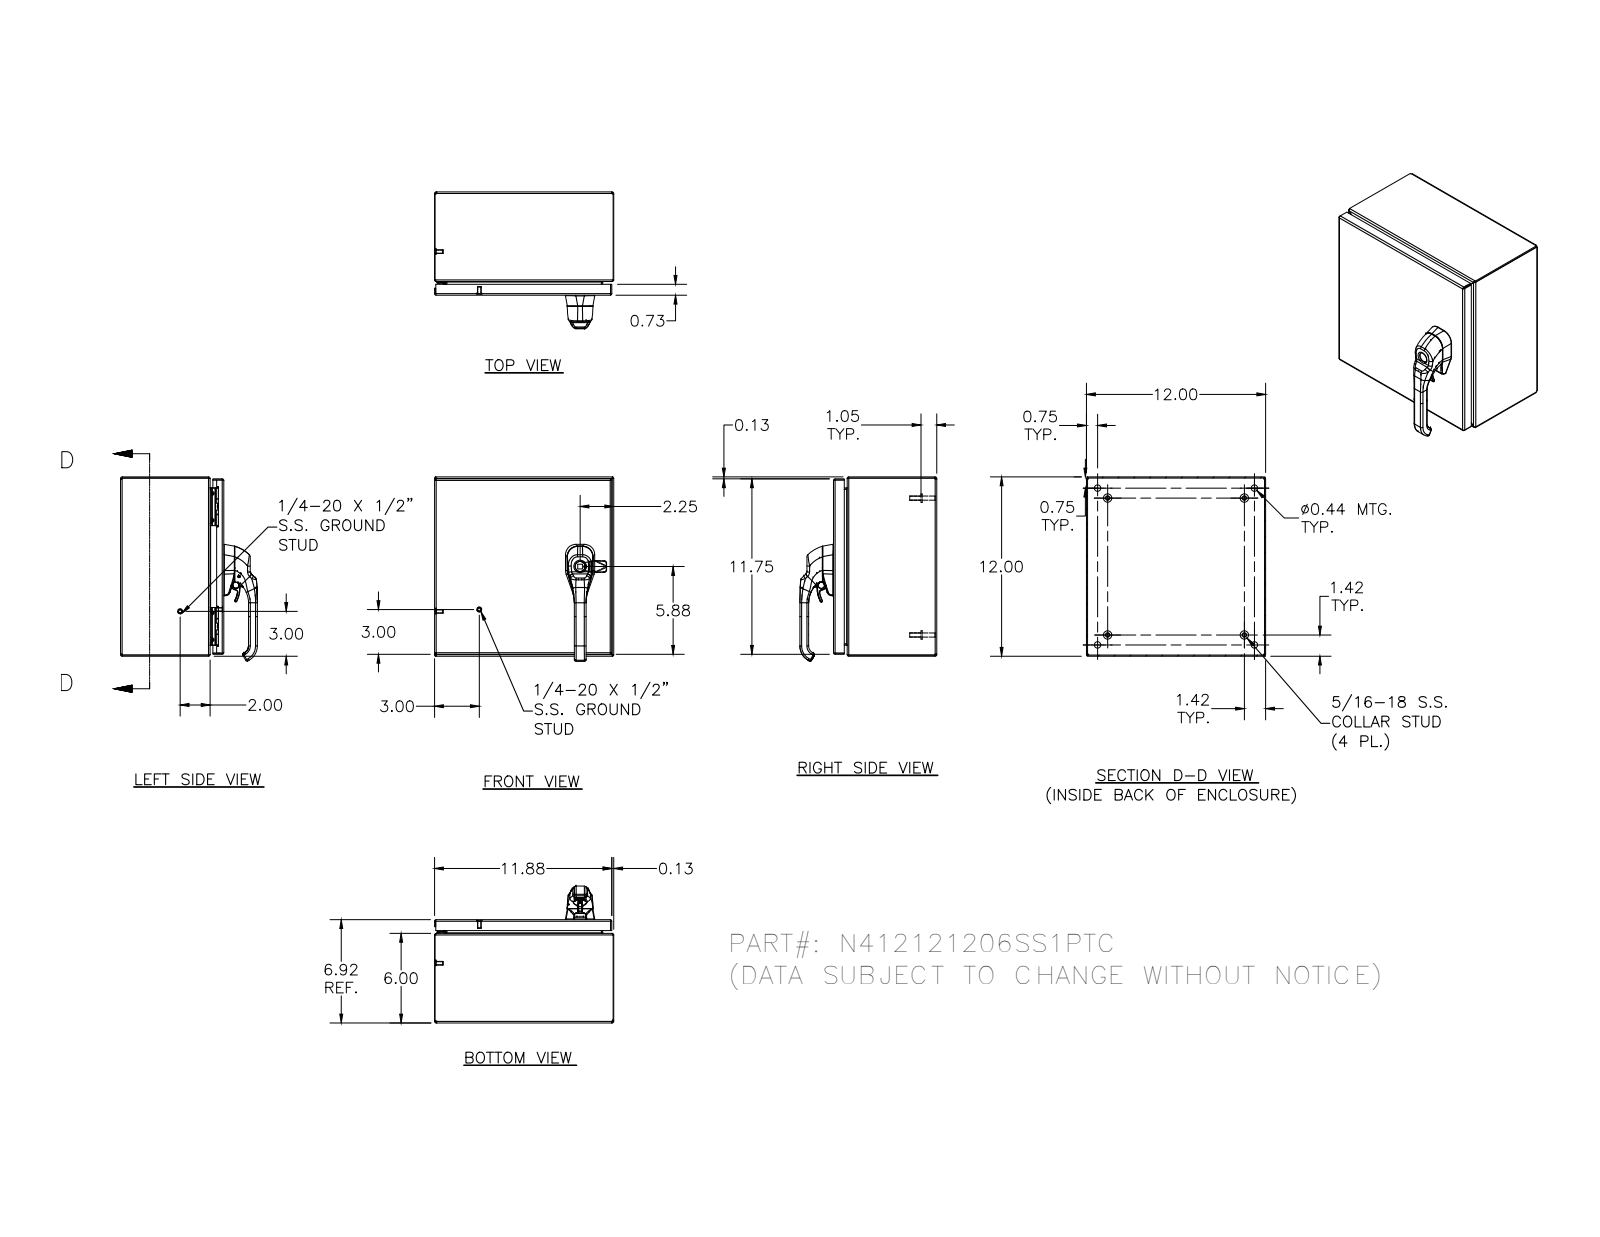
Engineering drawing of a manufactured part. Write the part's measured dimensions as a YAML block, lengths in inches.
part_name: "N412121206SS1PTC; N412121206SS1PTCBKP; N4121212SS1PTCLID; HFW328176 (+8 more)"
step_written_by: "Autodesk Inventor 2012 (AUTOMOTIVE_DESIGN)"
units: inches
bodies: {solids: 41, faces: 2782, planar: 882, cylindrical: 1035, other: 865}
overall_size: [12.34, 12, 9.166]
volume: 57.53
surface_area: 1469
round_holes:
  - {diameter: 0.093, count: 4}
  - {diameter: 0.152, count: 4}
  - {diameter: 0.167, count: 4}
  - {diameter: 0.172, count: 4}
  - {diameter: 0.188, count: 4}
  - {diameter: 0.437, count: 4}
  - {diameter: 0.213, count: 3}
  - {diameter: 0.281, count: 3}
  - {diameter: 0.156, count: 2}
  - {diameter: 0.315, count: 2}
  - {diameter: 0.402, count: 2}
  - {diameter: 0.413, count: 2}
round_bosses_or_shafts:
  - {diameter: 0.25, count: 10}
  - {diameter: 0.563, count: 4}
  - {diameter: 0.36, count: 4}
  - {diameter: 0.32, count: 4}
  - {diameter: 0.3, count: 4}
  - {diameter: 0.275, count: 4}
  - {diameter: 0.256, count: 4}
  - {diameter: 0.164, count: 4}
partial_cylinders:
  - {radius: 0.02, count: 173}
  - {radius: 0.012, count: 101}
  - {radius: 0.031, count: 30}
  - {radius: 0.05, count: 26}
  - {radius: 0.019, count: 21}
  - {radius: 0.105, count: 20}
  - {radius: 0.016, count: 18}
  - {radius: 0.079, count: 14}
face_to_face_distances: [0.074, 11.926, 6.843, 11.852, 12, 6.917, 6.769, 5.926, 0.917, 0.125]
hole_center_spacings: [7.996, 10.5, 0.017, 0.66, 8.656, 9.756, 0.019, 0.5]
